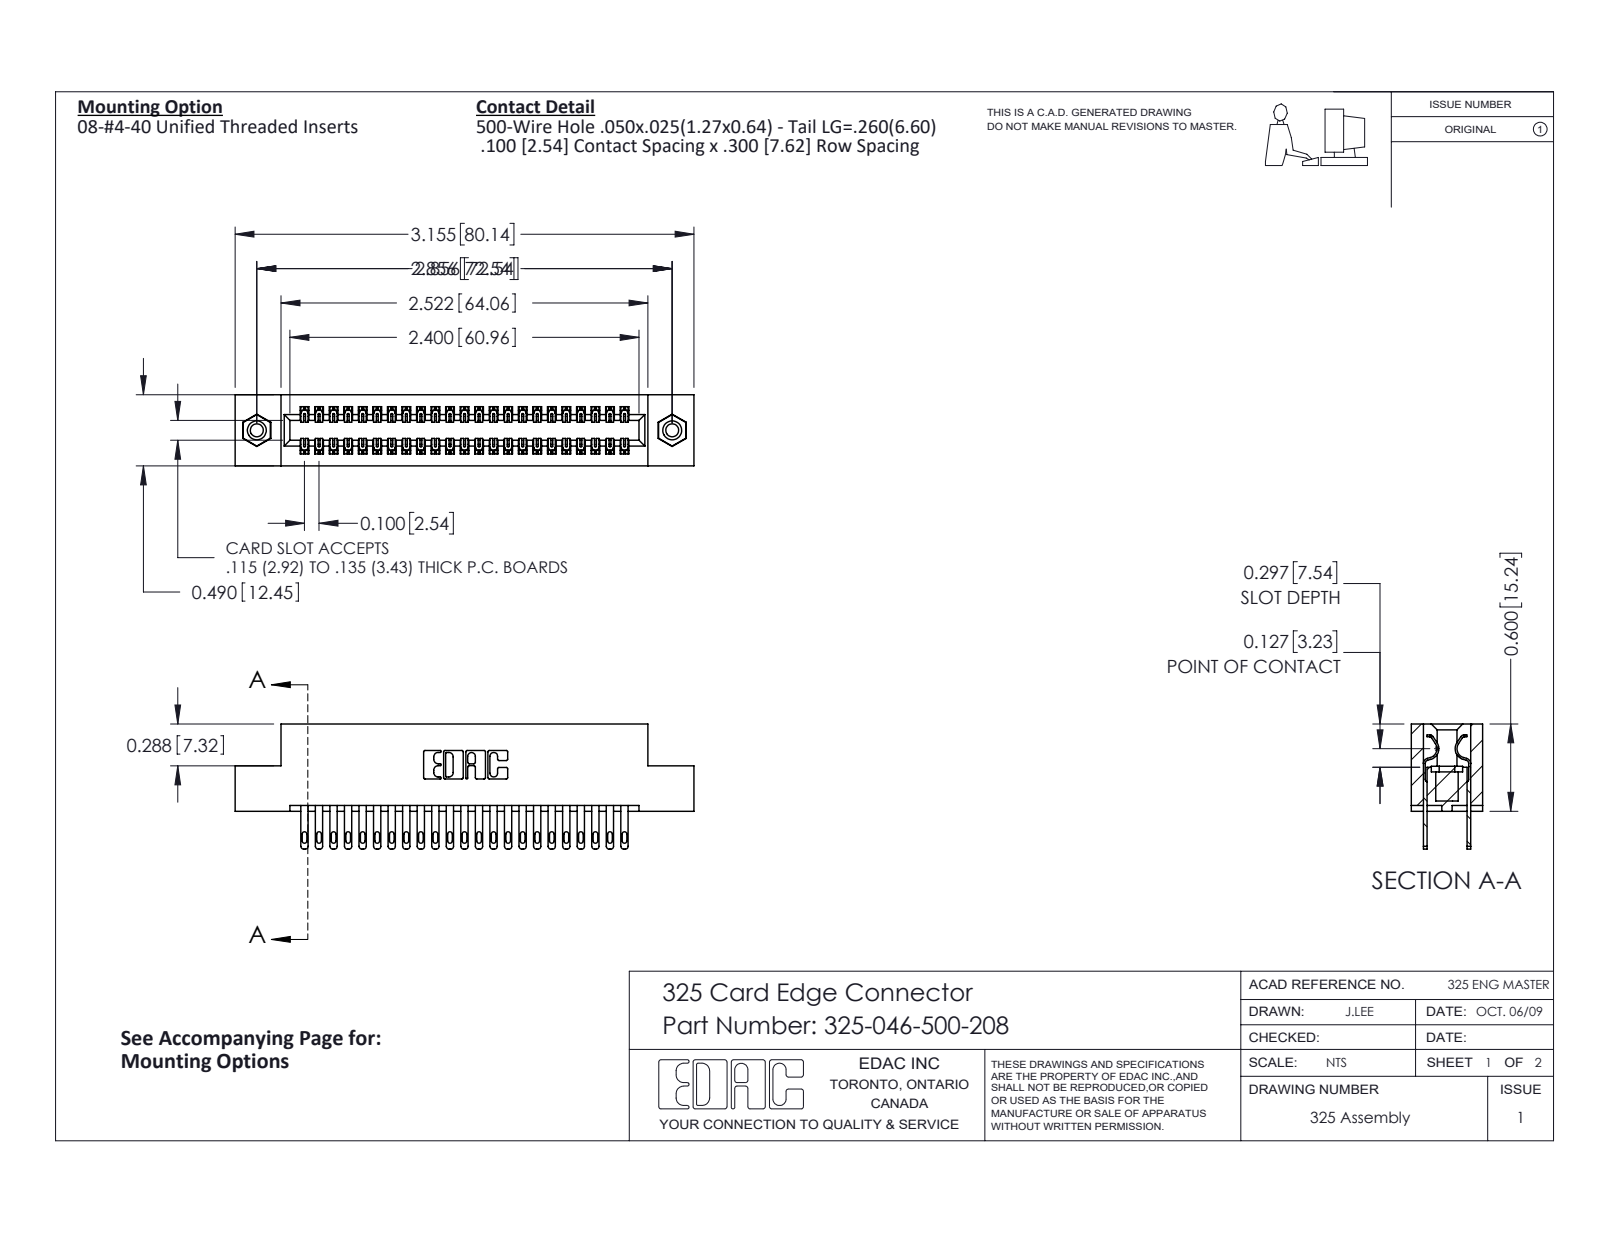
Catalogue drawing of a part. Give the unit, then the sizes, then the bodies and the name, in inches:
Units: inches
Overall size (bounding box): 3.155 × 0.86 × 0.49
Round holes (diameter × count): ⌀0.089 ×2, ⌀0.125 ×2, ⌀0.16 ×2
Round bosses / shafts (diameter × count): ⌀0.155 ×2
Partial cylindrical surfaces — rounded edges, fillets, slot ends (radius × count): R0.006 ×69, R0.016 ×46, R0.02 ×46, R0.01 ×22, R0.007 ×6, R0.031 ×6, R0.026 ×3, R0.014 ×2
Main face-to-face distances: 0.083, 0.407, 0.3, 0.107, 0.383, 0.025, 0.49, 0.325, 0.04, 0.275
Hole centre spacings: 2.856
Volume: 0.629 in³ · Surface area: 19.41 in²
Bodies: 49 solids, 2382 faces (1482 planar, 884 cylindrical, 16 other)
Part name (STEP PRODUCT): 325-046-500-208; 345-250-001_345-250-003-102; 325-292-001_325-293-100; 325 Part_TI
STEP written by: SolidWorks 2016 (CONFIG_CONTROL_DESIGN)
